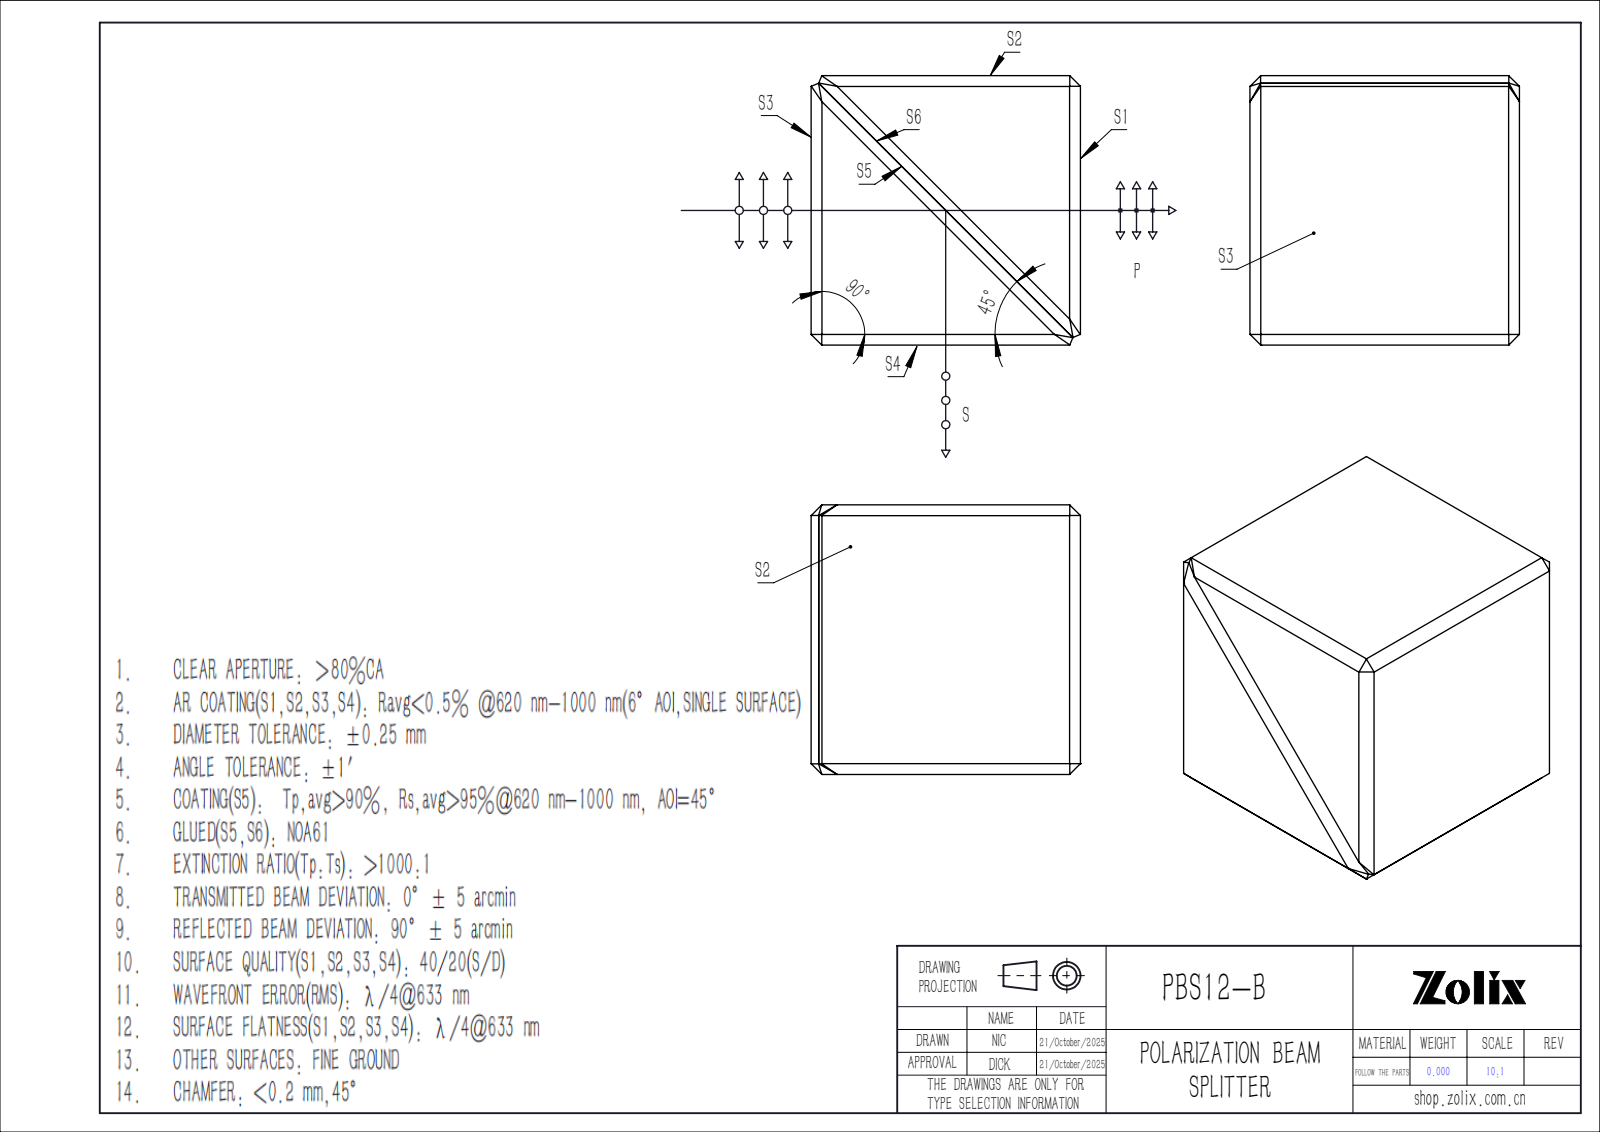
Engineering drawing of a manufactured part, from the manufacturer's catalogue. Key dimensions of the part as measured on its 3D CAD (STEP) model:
Part name (STEP PRODUCT): PBS622; PBS622-1-1; PBS622-1-2
STEP written by: SolidWorks 2022 (CONFIG_CONTROL_DESIGN)
Units: millimetres
Bodies: 2 solids, 43 faces (41 planar, 2 cylindrical, 0 other)
Overall size (bounding box): 12.7 × 12.7 × 12.7
Volume: 2 044 mm³ · Surface area: 1 388 mm²
Round holes (diameter × count): ⌀0.2 ×1
Main face-to-face distances: 12.7, 17.67, 8.7, 17.68, 8.84, 8.83, 16.22, 16.23, 18.81, 21.52
